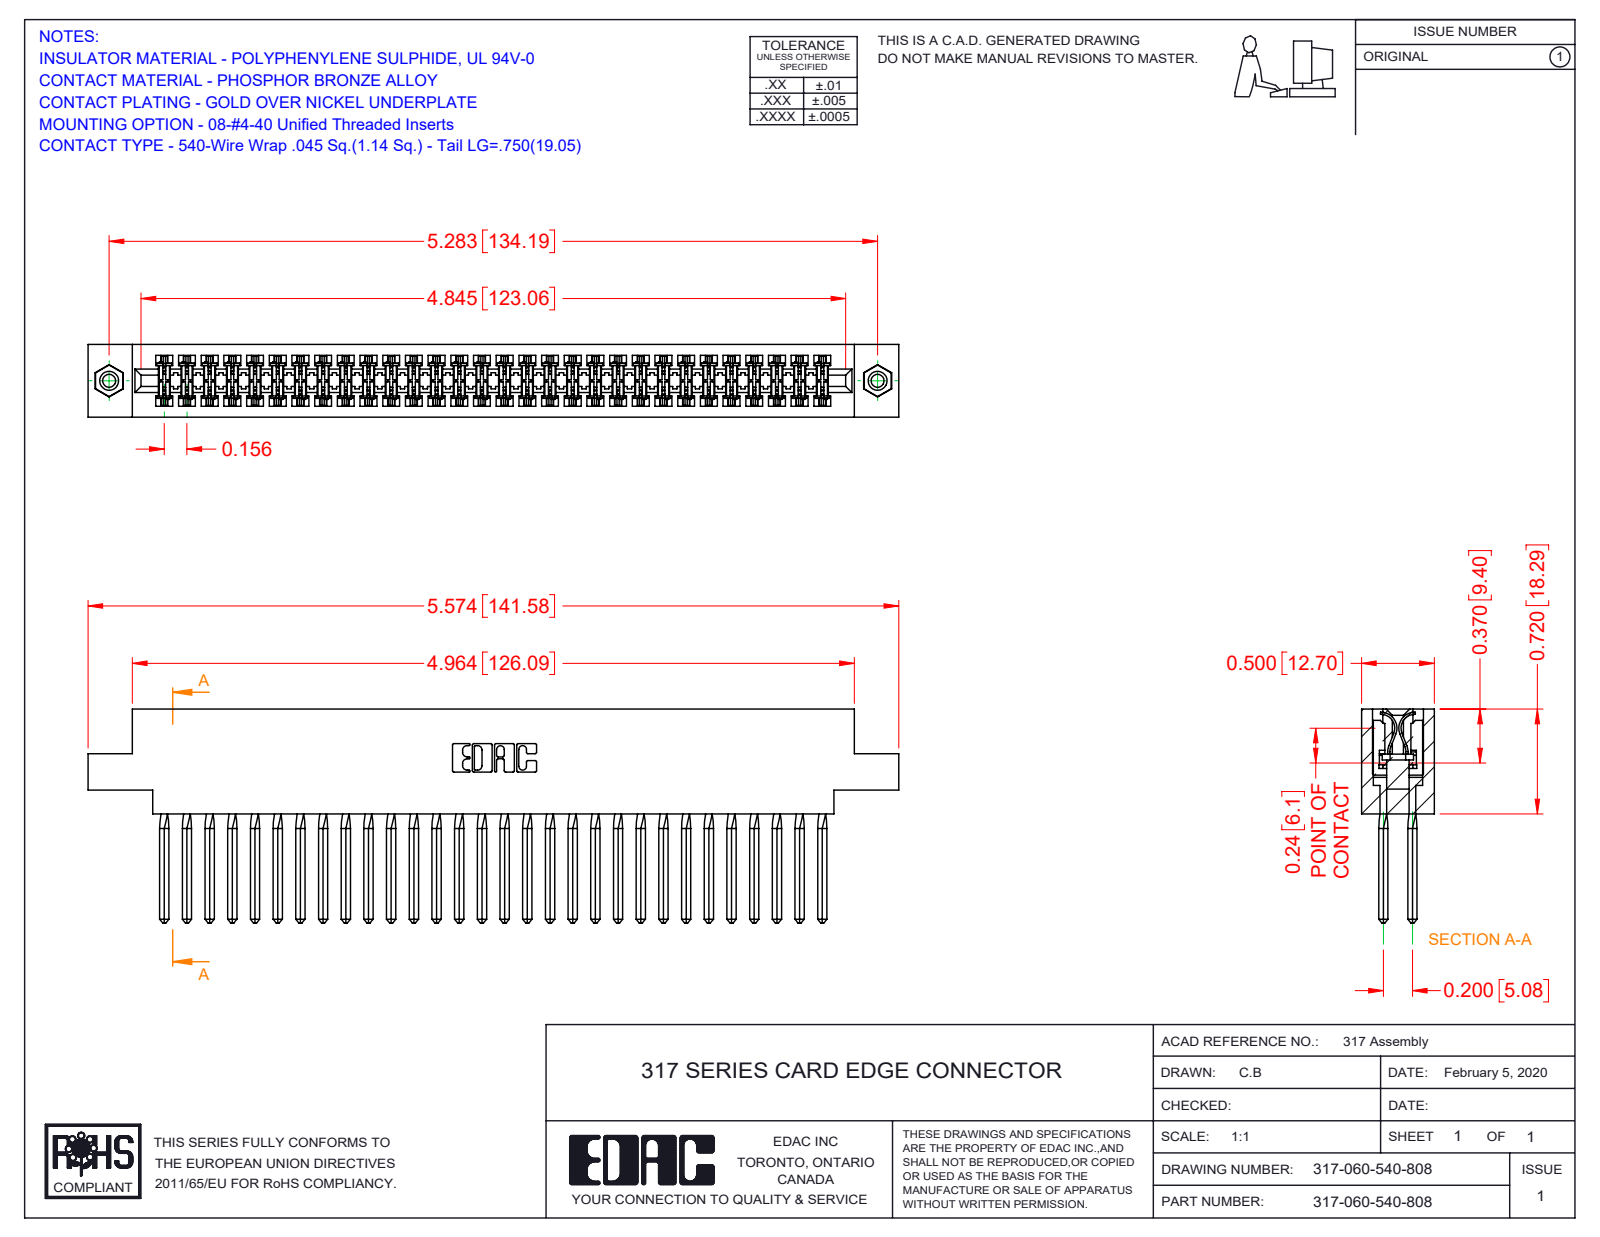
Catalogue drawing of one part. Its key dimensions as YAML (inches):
part_name: "345-250-001_345-250-003-102; 317-060-540-878; 317-290-001_540; 317 Part_.156 Dia - TI"
step_written_by: "SolidWorks 2016 (CONFIG_CONTROL_DESIGN)"
units: inches
bodies: {solids: 63, faces: 5502, planar: 4470, cylindrical: 776, other: 256}
overall_size: [5.574, 1.47, 0.5]
volume: 1.425
surface_area: 53.29
round_holes:
  - {diameter: 0.089, count: 2}
  - {diameter: 0.125, count: 2}
  - {diameter: 0.156, count: 2}
round_bosses_or_shafts:
  - {diameter: 0.155, count: 2}
partial_cylinders:
  - {radius: 0.015, count: 120}
  - {radius: 0.01, count: 22}
  - {radius: 0.007, count: 6}
  - {radius: 0.031, count: 6}
  - {radius: 0.026, count: 3}
  - {radius: 0.095, count: 2}
  - {radius: 0.1, count: 2}
  - {radius: 0.11, count: 2}
face_to_face_distances: [0.5, 0.075, 0.425, 0.35, 0.11, 0.195, 0.094, 0.2, 0.72, 0.115]
hole_center_spacings: [5.283]
